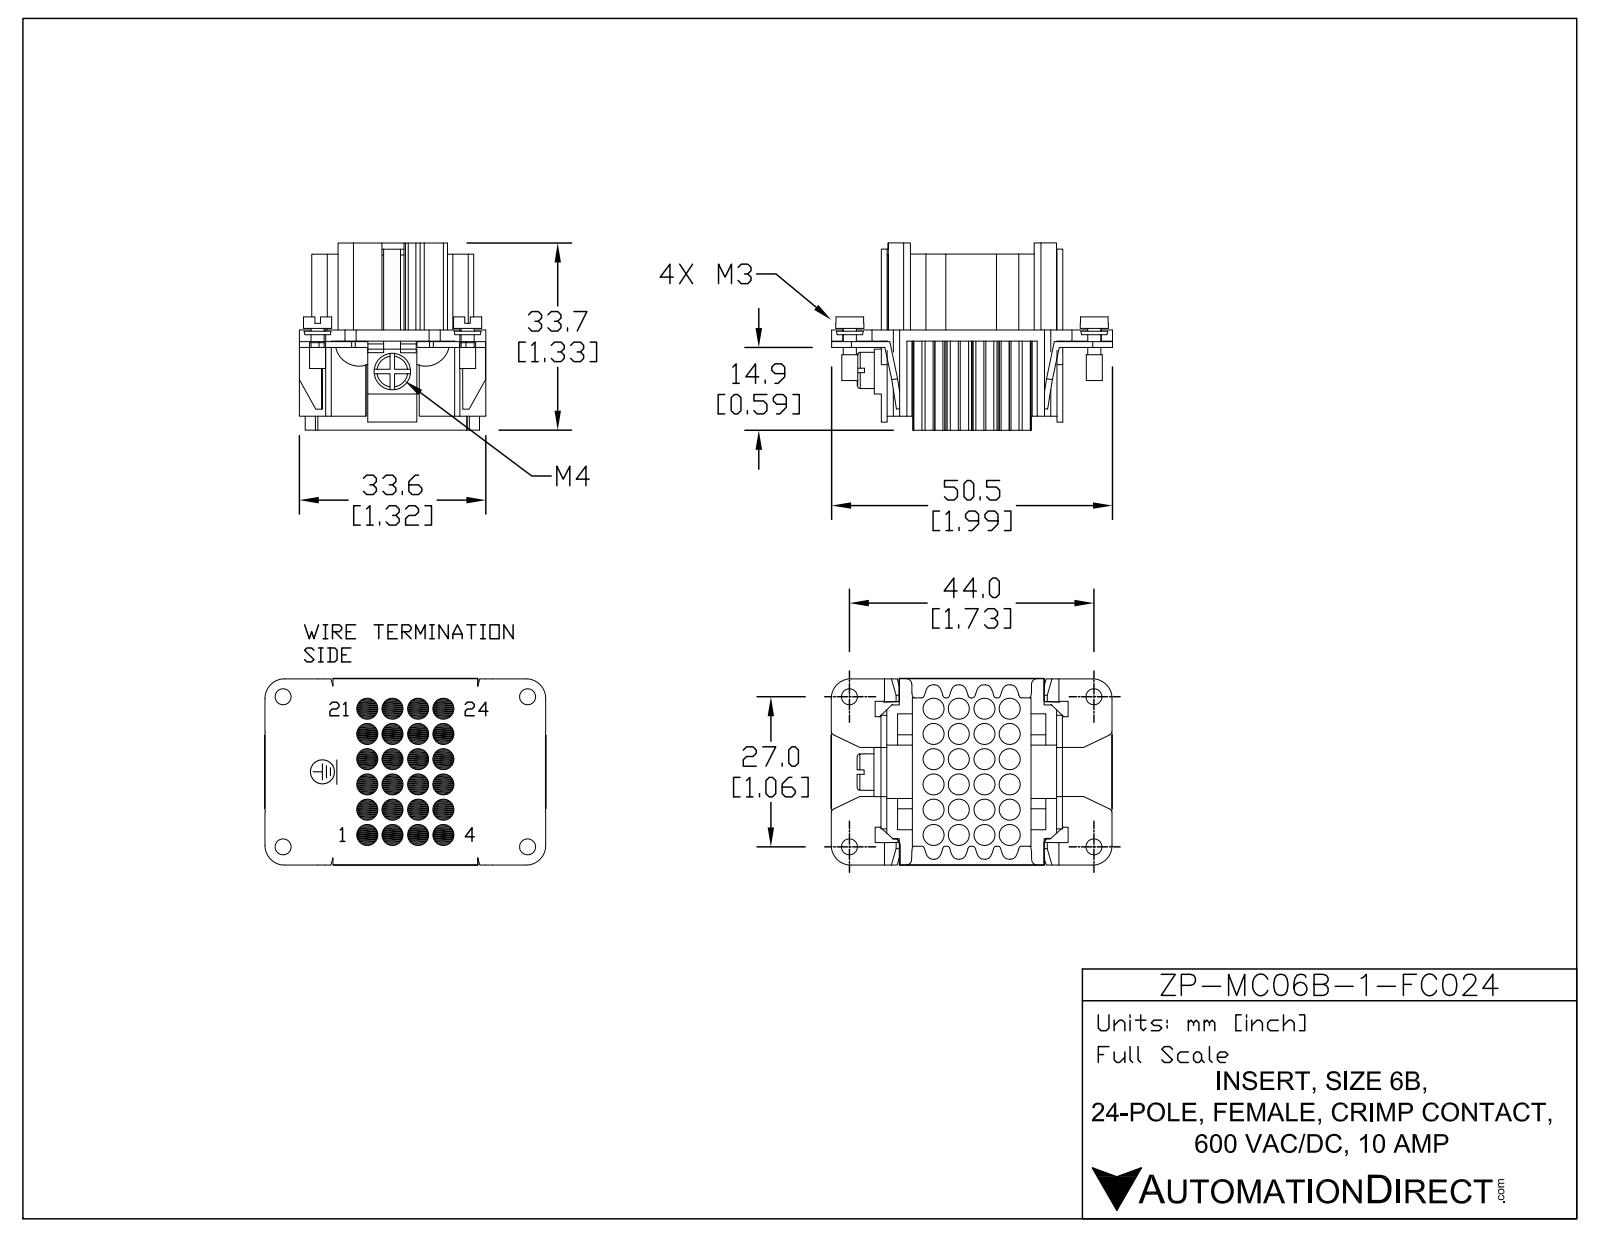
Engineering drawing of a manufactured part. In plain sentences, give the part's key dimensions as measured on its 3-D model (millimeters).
The part is named "ZP-6B-24-FC-INSERT". Its 3-D file was written by "SolidWorks 2011 (AUTOMOTIVE_DESIGN)". It is 5 solids with 512 faces: 362 planar, 62 cylindrical and 88 other. Overall it measures 50.01 by 36 by 33.25 millimeters. Its volume is 17 653 cubic millimeters and its surface area 21 574 square millimeters. Round holes: 24 of diameter 3.75, 4 of diameter 2.5, 1 of diameter 3. Round bosses or shafts: 4 of diameter 5.02, 4 of diameter 2.85, 4 of diameter 2.32, 1 of diameter 6.5. Partial cylindrical surfaces (rounded edges, fillets, slot ends): 4 of radius 0.75, 4 of radius 3.5, 2 of radius 5.75, 1 of radius 0.37, 1 of radius 0.39, 1 of radius 0.4, 1 of radius 1.99. The main face-to-face distances are 1.05, 2, 26.68, 2.07, 16, 18, 5.61, 1.04, 3.12, 1.12. The hole center spacings are 10.06, 4.5, 6.36, 9, 14.23, 16.22, 13.5, 12.73.
